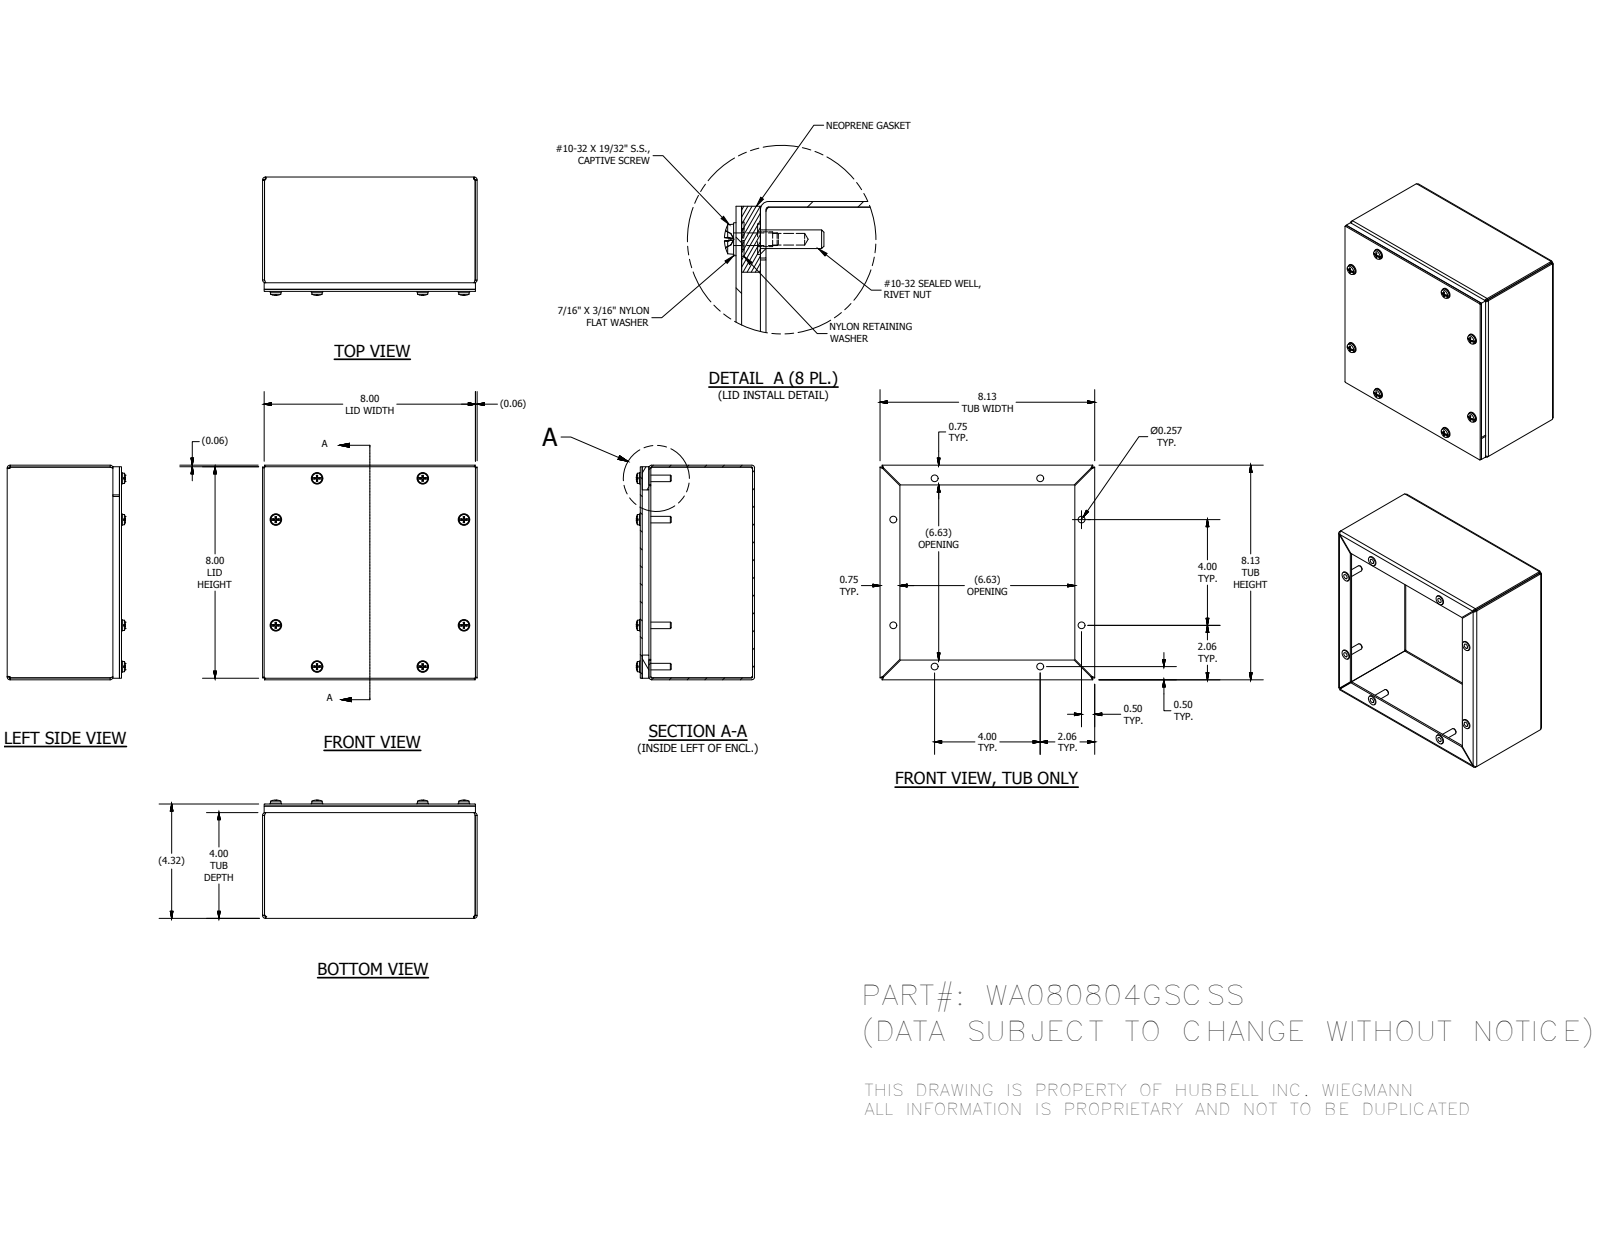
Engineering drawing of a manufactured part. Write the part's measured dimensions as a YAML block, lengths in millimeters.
part_name: "WA080804GSCSSBKP; WA0808GSCSSLID; 316280; 37210 (+4 more)"
step_written_by: "Autodesk Inventor 2016 (AUTOMOTIVE_DESIGN)"
units: millimeters
bodies: {solids: 36, faces: 764, planar: 420, cylindrical: 160, other: 184}
overall_size: [206.38, 206.38, 113.75]
volume: 438091
surface_area: 412701
round_holes:
  - {diameter: 3.96, count: 8}
  - {diameter: 4.78, count: 8}
  - {diameter: 4.98, count: 8}
  - {diameter: 6.53, count: 8}
  - {diameter: 7.06, count: 8}
  - {diameter: 7.14, count: 8}
  - {diameter: 7.95, count: 8}
round_bosses_or_shafts:
  - {diameter: 11.51, count: 8}
  - {diameter: 11.11, count: 8}
  - {diameter: 10.31, count: 8}
  - {diameter: 6.3, count: 8}
  - {diameter: 4.25, count: 8}
partial_cylinders:
  - {radius: 0.79, count: 12}
  - {radius: 1.78, count: 8}
  - {radius: 2.27, count: 8}
  - {radius: 2.67, count: 8}
face_to_face_distances: [1.88, 107.95, 204.5, 109.83, 106.07, 99.72, 8.23, 206.38, 202.62, 6.35]
hole_center_spacings: [101.6, 56.12, 146.73, 146.74, 146.75, 146.76, 180.96, 199.8]
